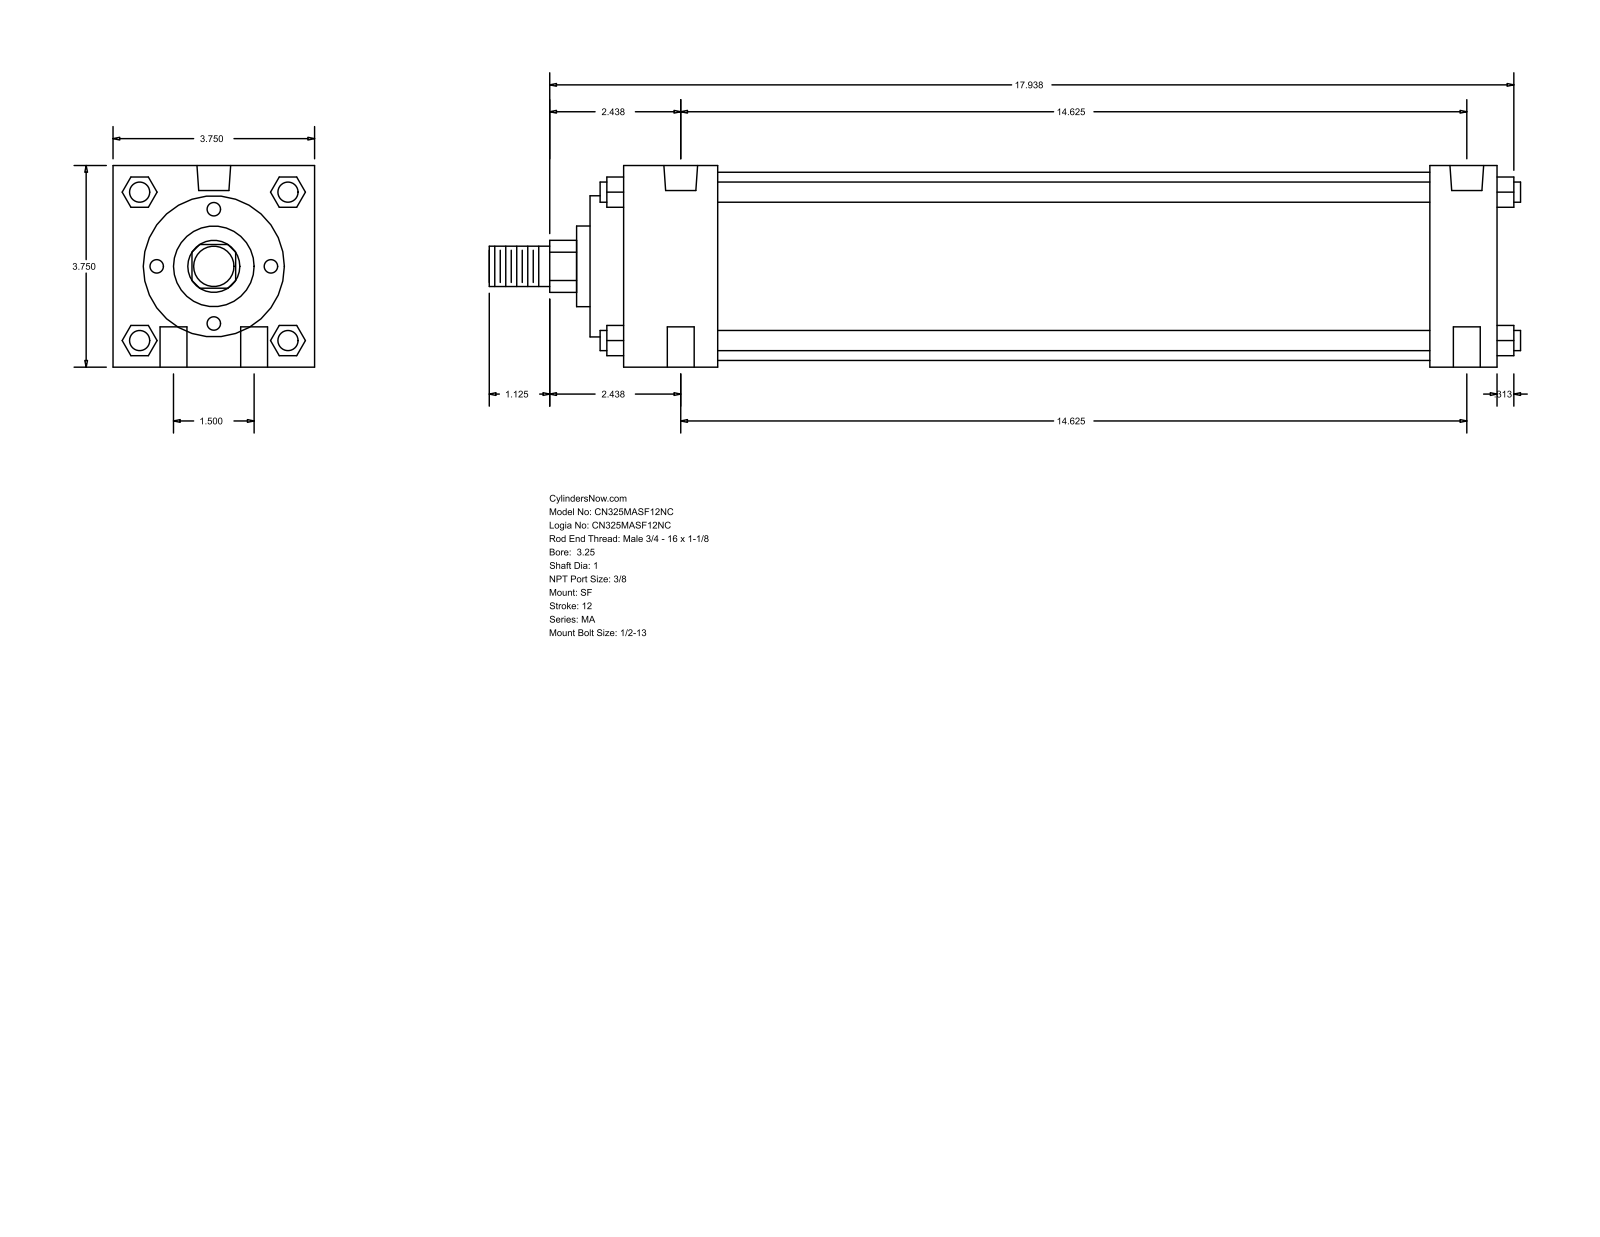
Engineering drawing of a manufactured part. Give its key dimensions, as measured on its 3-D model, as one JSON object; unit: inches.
{"part_name": "MA_SF__0325_1", "step_written_by": "GSSL Pune (CONFIG_CONTROL_DESIGN)", "units": "inches", "bodies": {"solids": 0, "faces": 126, "planar": 95, "cylindrical": 31, "other": 0}, "overall_size": [19.187, 3.75, 3.75], "round_holes": [[0.5, 4], [0.437, 2], [0.627, 2]], "round_bosses_or_shafts": [[0.375, 4], [3.5, 1], [2.625, 1], [1.5, 1], [1, 1], [0.75, 1]], "partial_cylinders_radius": [[0.484, 1]], "face_to_face_distances": [3.75, 16.25, 15, 1.25, 1.75, 13.25, 14.5, 0.625, 2.375, 15.625], "hole_center_spacings": [0.75, 14.644, 14.625, 1.5, 14.702, 14.25]}
